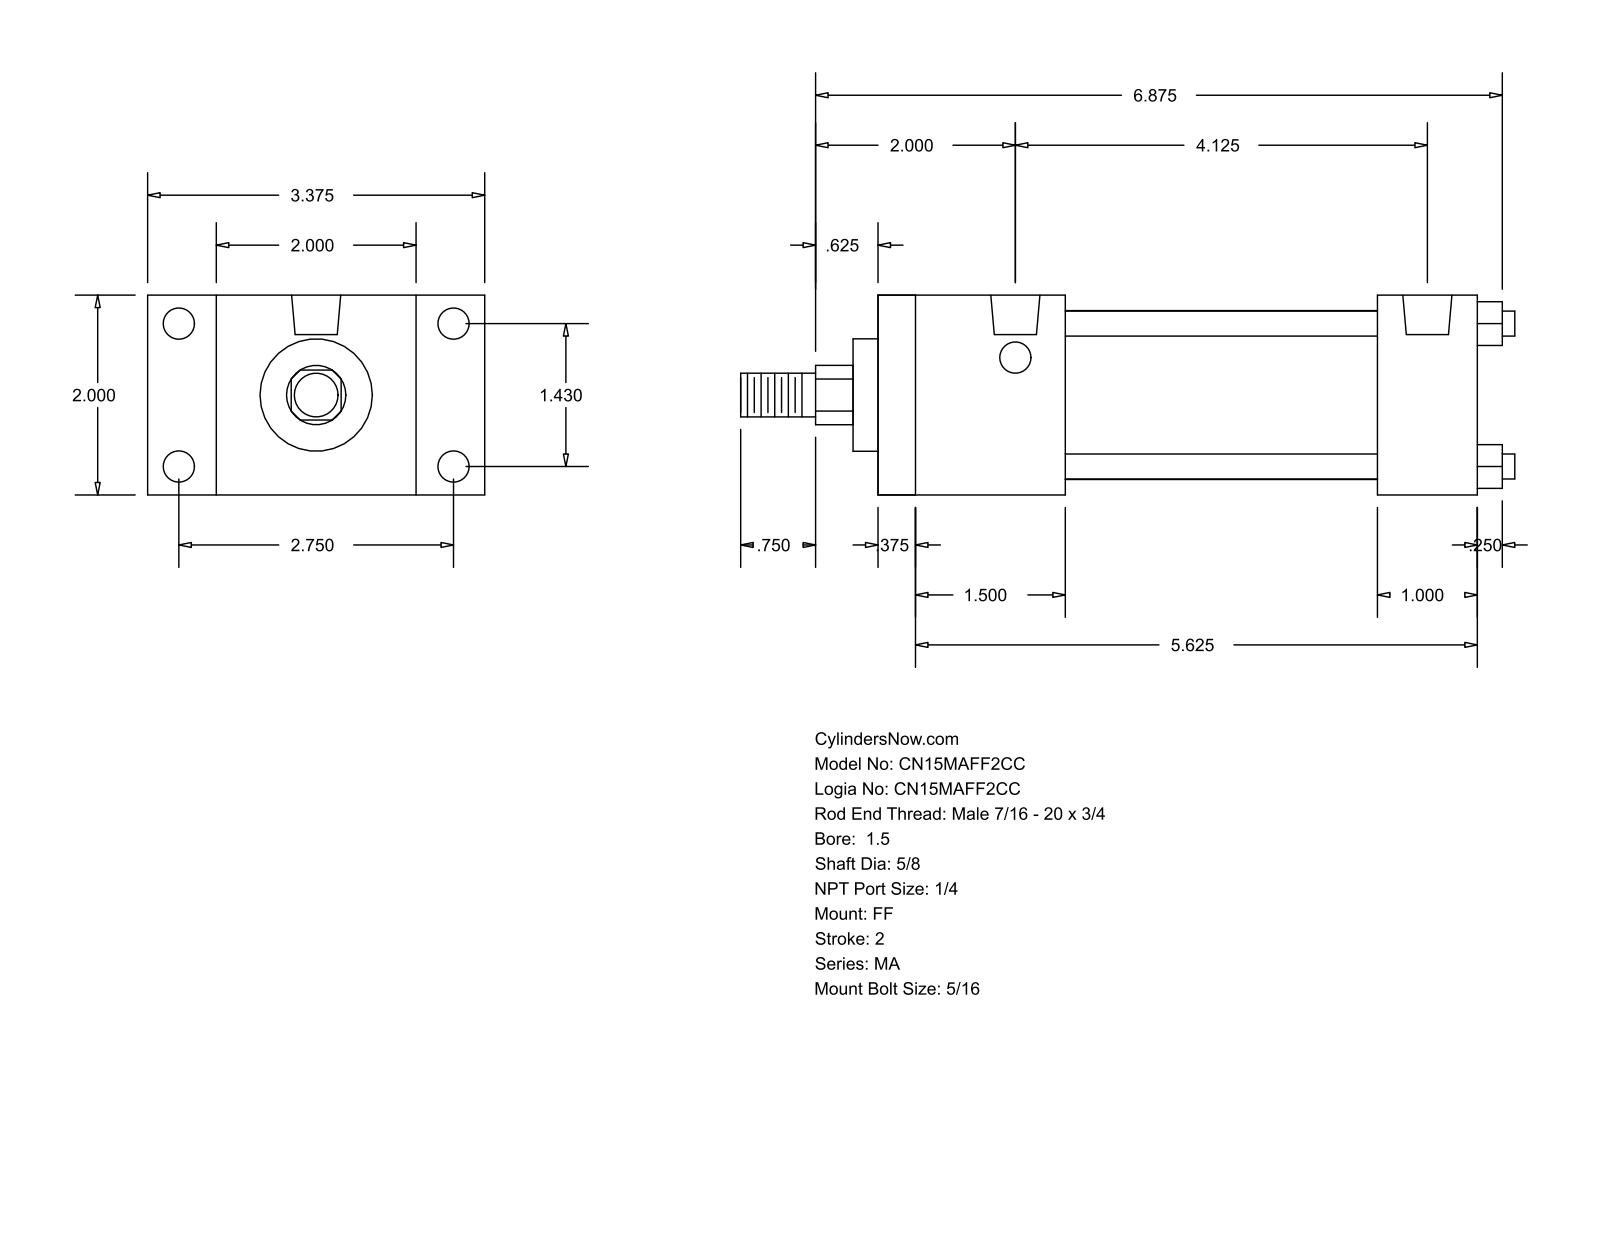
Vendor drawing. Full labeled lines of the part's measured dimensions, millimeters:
Part name (STEP PRODUCT): MA_FF__0150_0.625
STEP written by: GSSL Pune (CONFIG_CONTROL_DESIGN)
Units: millimetres
Bodies: 0 solids, 92 faces (64 planar, 28 cylindrical, 0 other)
Overall size (bounding box): 196.85 × 85.72 × 50.8
Round holes (diameter × count): ⌀7.94 ×8, ⌀12.49 ×2
Round bosses / shafts (diameter × count): ⌀6.35 ×4, ⌀42.93 ×1, ⌀28.57 ×1, ⌀15.88 ×1, ⌀11.11 ×1
Partial cylindrical surfaces — rounded edges, fillets, slot ends (radius × count): R7.54 ×1
Main face-to-face distances: 50.8, 152.4, 9.52, 142.88, 25.4, 47.62, 127, 38.1, 117.48, 79.38
Hole centre spacings: 36.32, 69.84, 78.72, 104.77
